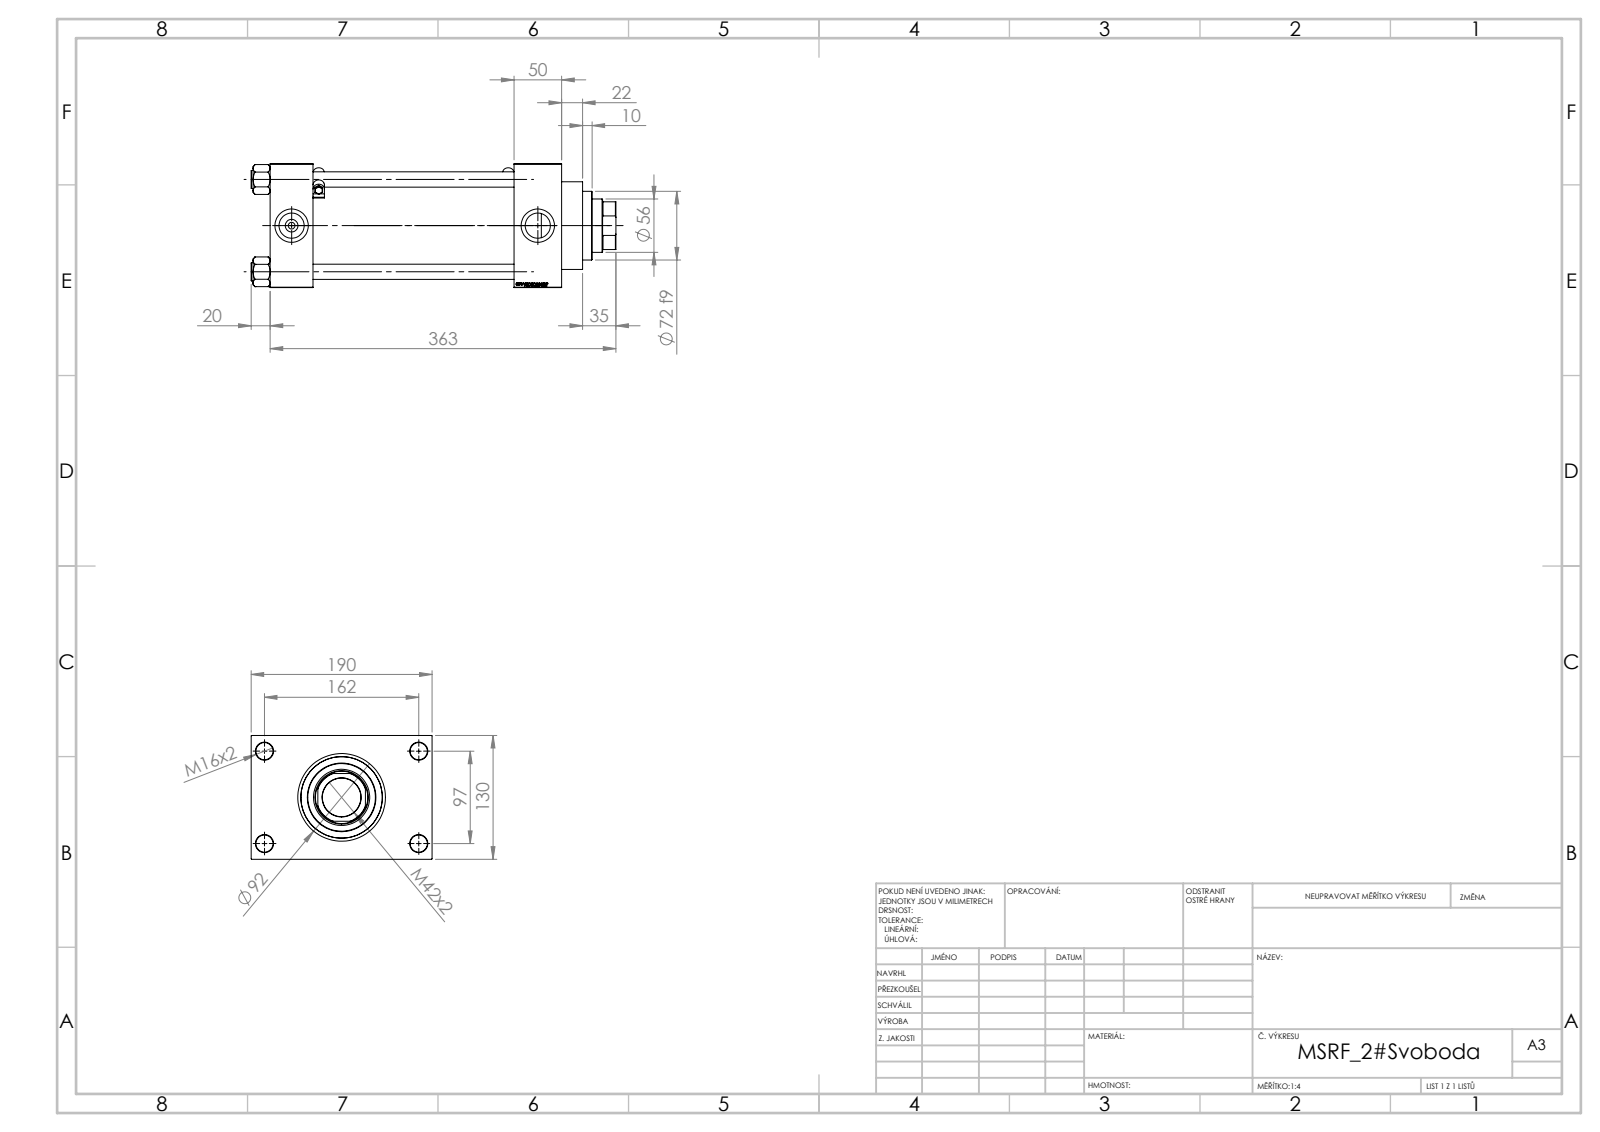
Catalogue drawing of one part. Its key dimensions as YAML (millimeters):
part_name: "MSRF_MSRG1; V215CR_D_Body; V215CR_D_TYCINKA; V215_VC_A (+2 more)"
step_written_by: "SolidWorks 2019 (CONFIG_CONTROL_DESIGN)"
units: millimeters
bodies: {solids: 13, faces: 1215, planar: 581, cylindrical: 116, other: 518}
overall_size: [383, 190, 130]
volume: 3229000
surface_area: 510455
round_holes:
  - {diameter: 16, count: 4}
  - {diameter: 18, count: 4}
  - {diameter: 7, count: 2}
  - {diameter: 26.44, count: 2}
  - {diameter: 35, count: 2}
  - {diameter: 40.5, count: 1}
  - {diameter: 56, count: 1}
  - {diameter: 59, count: 1}
  - {diameter: 76, count: 1}
  - {diameter: 85.5, count: 1}
  - {diameter: 100, count: 1}
round_bosses_or_shafts:
  - {diameter: 19, count: 4}
  - {diameter: 5, count: 2}
  - {diameter: 2.5, count: 2}
  - {diameter: 106, count: 1}
  - {diameter: 92, count: 1}
  - {diameter: 72, count: 1}
partial_cylinders:
  - {radius: 0.5, count: 12}
  - {radius: 6, count: 4}
  - {radius: 27, count: 1}
face_to_face_distances: [130, 50, 45, 256, 211, 306, 261, 160, 30, 190]
hole_center_spacings: [32.55, 68.52, 94.41, 96.9, 102.27, 129.45, 161.73, 97]
